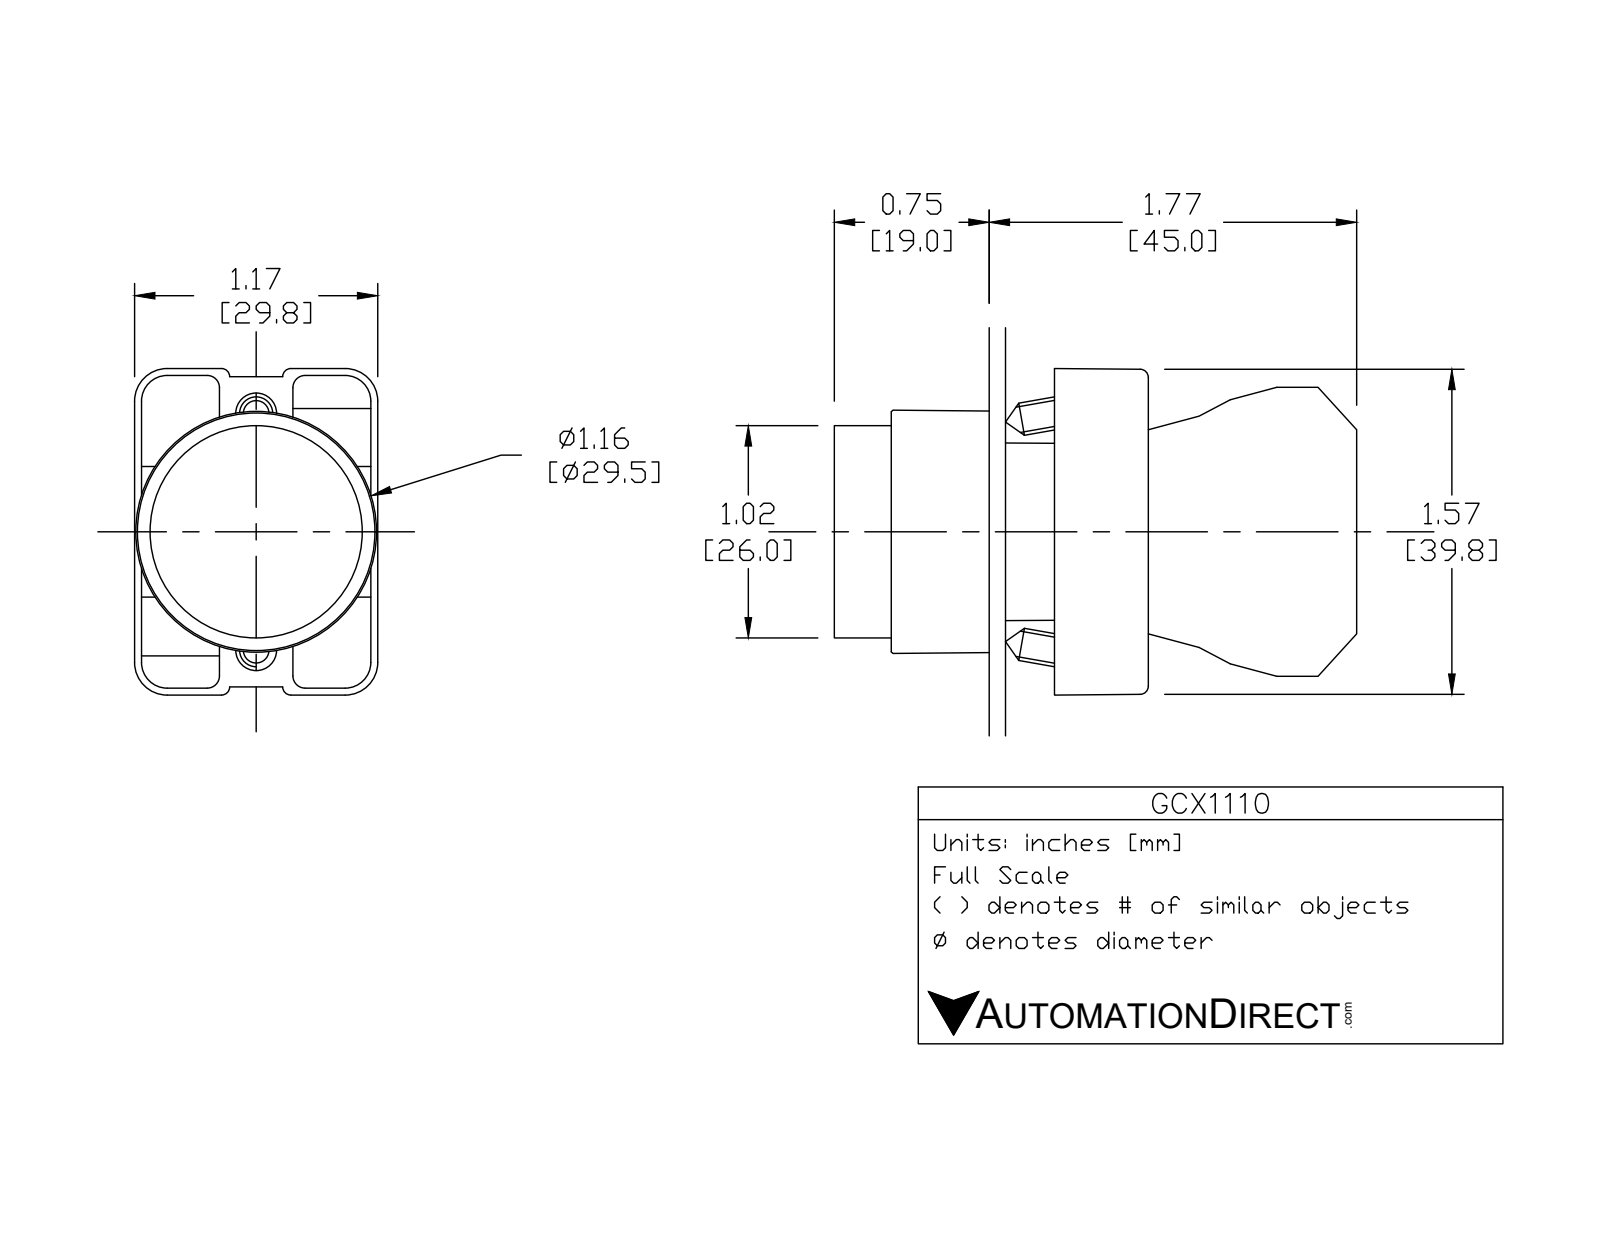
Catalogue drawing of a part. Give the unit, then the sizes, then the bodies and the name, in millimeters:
Units: millimetres
Overall size (bounding box): 63.3 × 40.2 × 29.9
Round holes (diameter × count): ⌀2 ×2, ⌀3.1 ×2, ⌀3.3 ×2, ⌀2.2 ×1, ⌀5 ×1, ⌀22.3 ×1, ⌀22.6 ×1, ⌀26 ×1
Round bosses / shafts (diameter × count): ⌀4 ×2, ⌀29.8 ×1, ⌀25.5 ×1, ⌀24 ×1, ⌀21.7 ×1, ⌀19.8 ×1
Partial cylindrical surfaces — rounded edges, fillets, slot ends (radius × count): R1.5 ×24, R1 ×12, R3.1 ×12, R4 ×12, R1 ×4, R3.3 ×2, R0.5 ×1, R1.6 ×1
Main face-to-face distances: 14.7, 0.8, 30.3, 0.8, 12, 18.3, 7, 17.5, 15.2, 29.5
Hole centre spacings: 6, 13.8, 12, 12.4
Volume: 25 960 mm³ · Surface area: 17 080 mm²
Bodies: 6 solids, 383 faces (222 planar, 132 cylindrical, 29 other)
Part name (STEP PRODUCT): ecx1040; GCX1110; ecx1029; GCX1110 OPERATOR
STEP written by: SolidWorks 2016 (AUTOMOTIVE_DESIGN)
